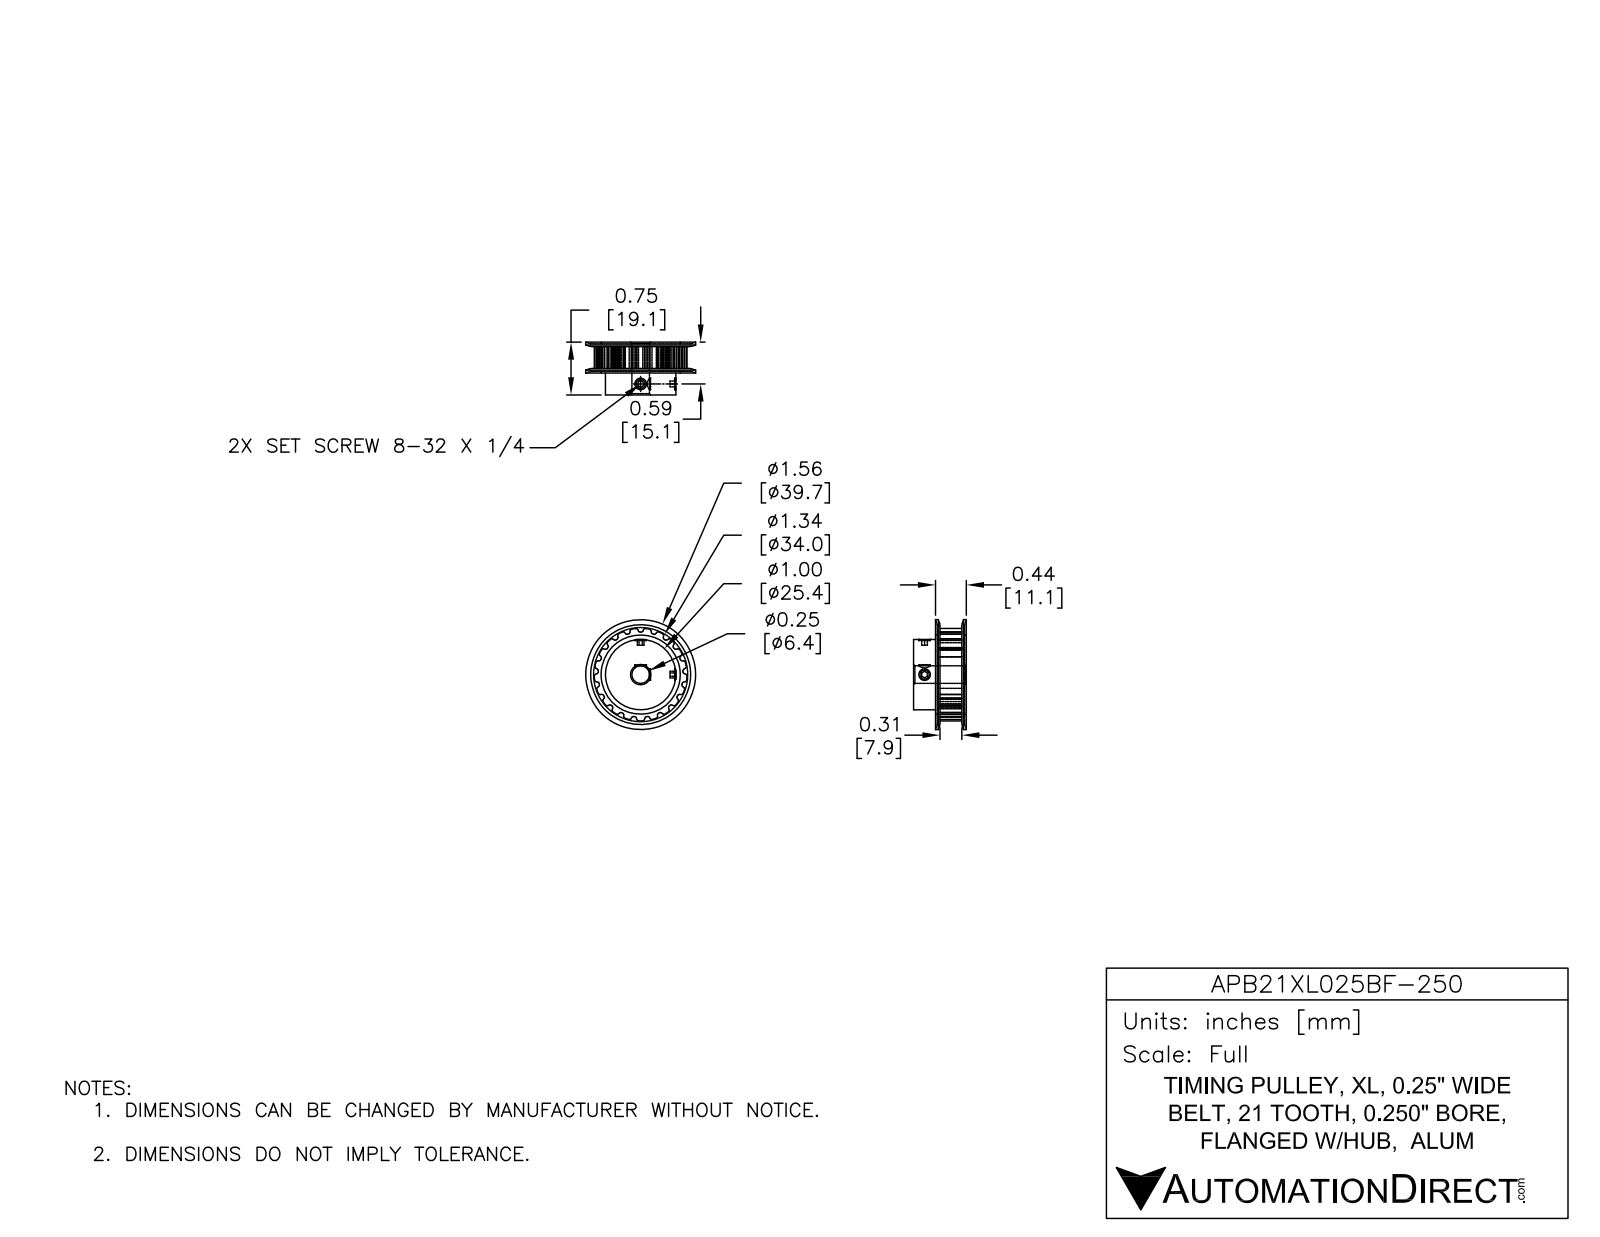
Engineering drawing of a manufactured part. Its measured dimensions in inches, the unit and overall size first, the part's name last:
Units: inches
Overall size (bounding box): 1.563 × 1.563 × 0.75
Round holes (diameter × count): ⌀0.088 ×2, ⌀0.25 ×1
Round bosses / shafts (diameter × count): ⌀1 ×1
Partial cylindrical surfaces — rounded edges, fillets, slot ends (radius × count): R0.015 ×84, R0.604 ×1
Main face-to-face distances: 0.343, 0.033, 0.375, 0.75, 0.407, 0.717, 0.342, 0.375, 0.065, 0.032
Volume: 0.773 in³ · Surface area: 8.905 in²
Bodies: 1 solid, 223 faces (69 planar, 132 cylindrical, 22 other)
Part name (STEP PRODUCT): APB21XL025BF-250
STEP written by: SolidWorks 2014 (AUTOMOTIVE_DESIGN)
